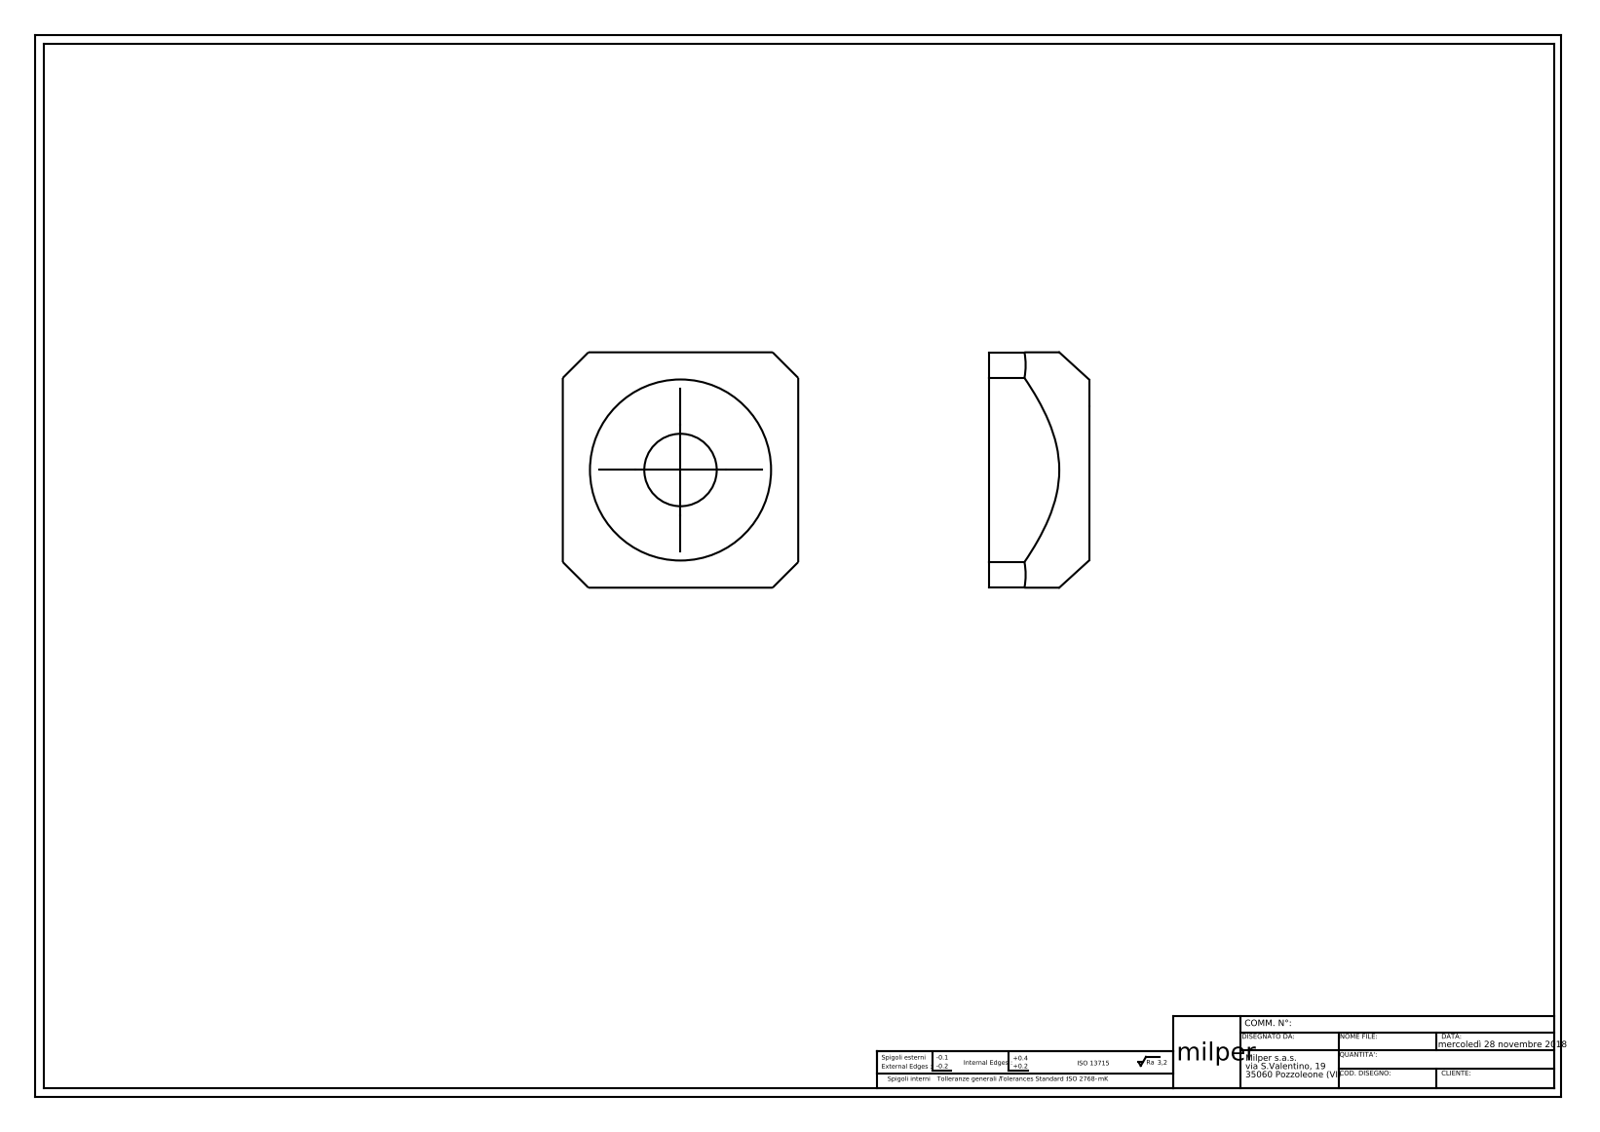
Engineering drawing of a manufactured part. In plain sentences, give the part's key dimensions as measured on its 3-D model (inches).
The part is named "dado-M4-3D". Its 3-D file was written by "SolidWorks 2018 (CONFIG_CONTROL_DESIGN)". It is 1 solid with 14 faces: 10 planar, 2 cylindrical and 2 other. Overall it measures 0.512 by 0.512 by 0.217 inches. Its volume is 0.044 cubic inches and its surface area 0.87 square inches. Round holes: 1 of diameter 0.157. The main face-to-face distances are 0.217, 0.512, 0.645.
